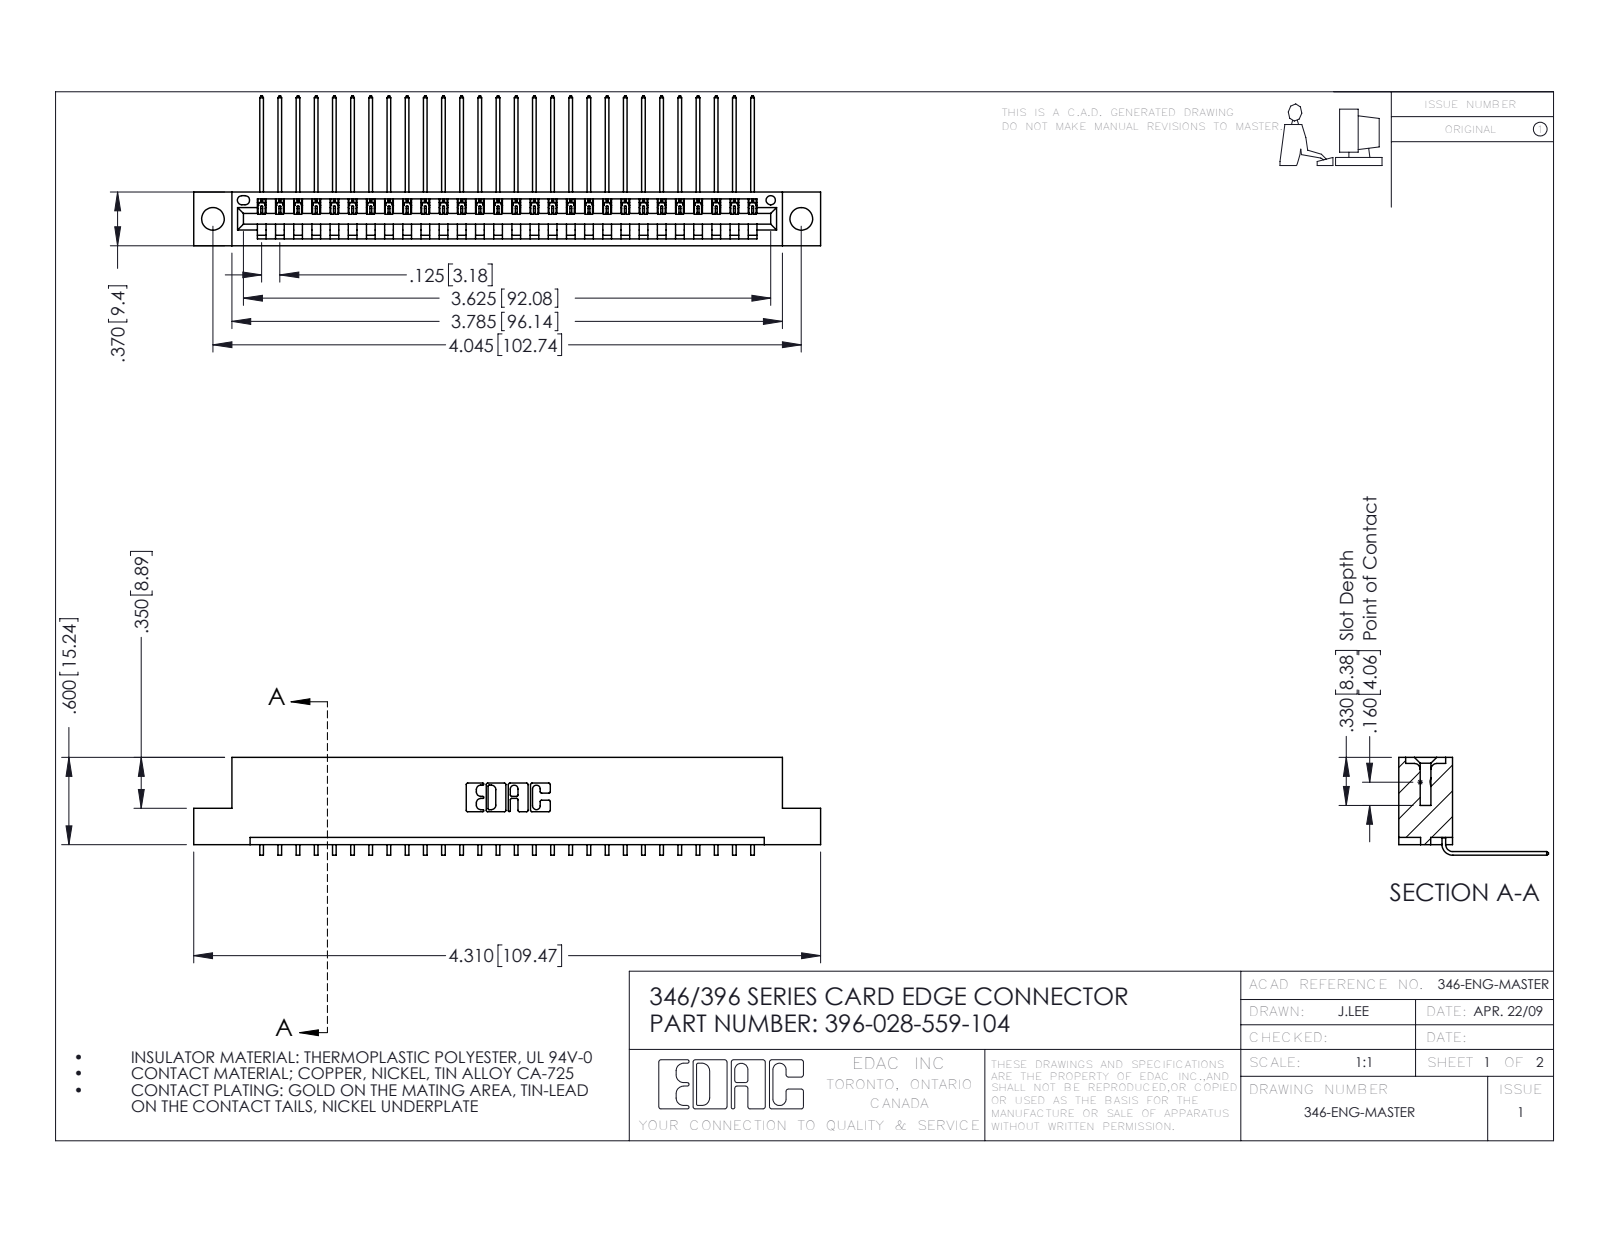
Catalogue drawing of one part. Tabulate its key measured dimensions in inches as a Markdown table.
| quantity | value |
| --- | --- |
| part name | 345-292-001_558 559 Tail - 1; 396-028-559-104; 346 Part_Flush Mounting Lugs - 0.156 Dia-TH |
| STEP written by | SolidWorks 2016 (CONFIG_CONTROL_DESIGN) |
| units | inches |
| bodies | 29 solids, 1802 faces (1252 planar, 550 cylindrical, 0 other) |
| overall size | 4.31 × 1.03 × 0.673 |
| volume | 0.634 in³ |
| surface area | 20.45 in² |
| round holes (diameter × count) | 0.156 × 2, 0.064 × 1 |
| partial cylindrical surfaces (radius × count) | 0.006 × 56, 0.01 × 22, 0.007 × 6, 0.031 × 6, 0.026 × 3, 0.031 × 2, 0.04 × 2, 0.014 × 1 |
| main face-to-face distances | 0.048, 0.322, 0.37, 0.25, 0.072, 0.025, 0.298, 0.148, 0.222, 0.1 |
| hole center spacings | 0.246, 3.837, 4.045 |
